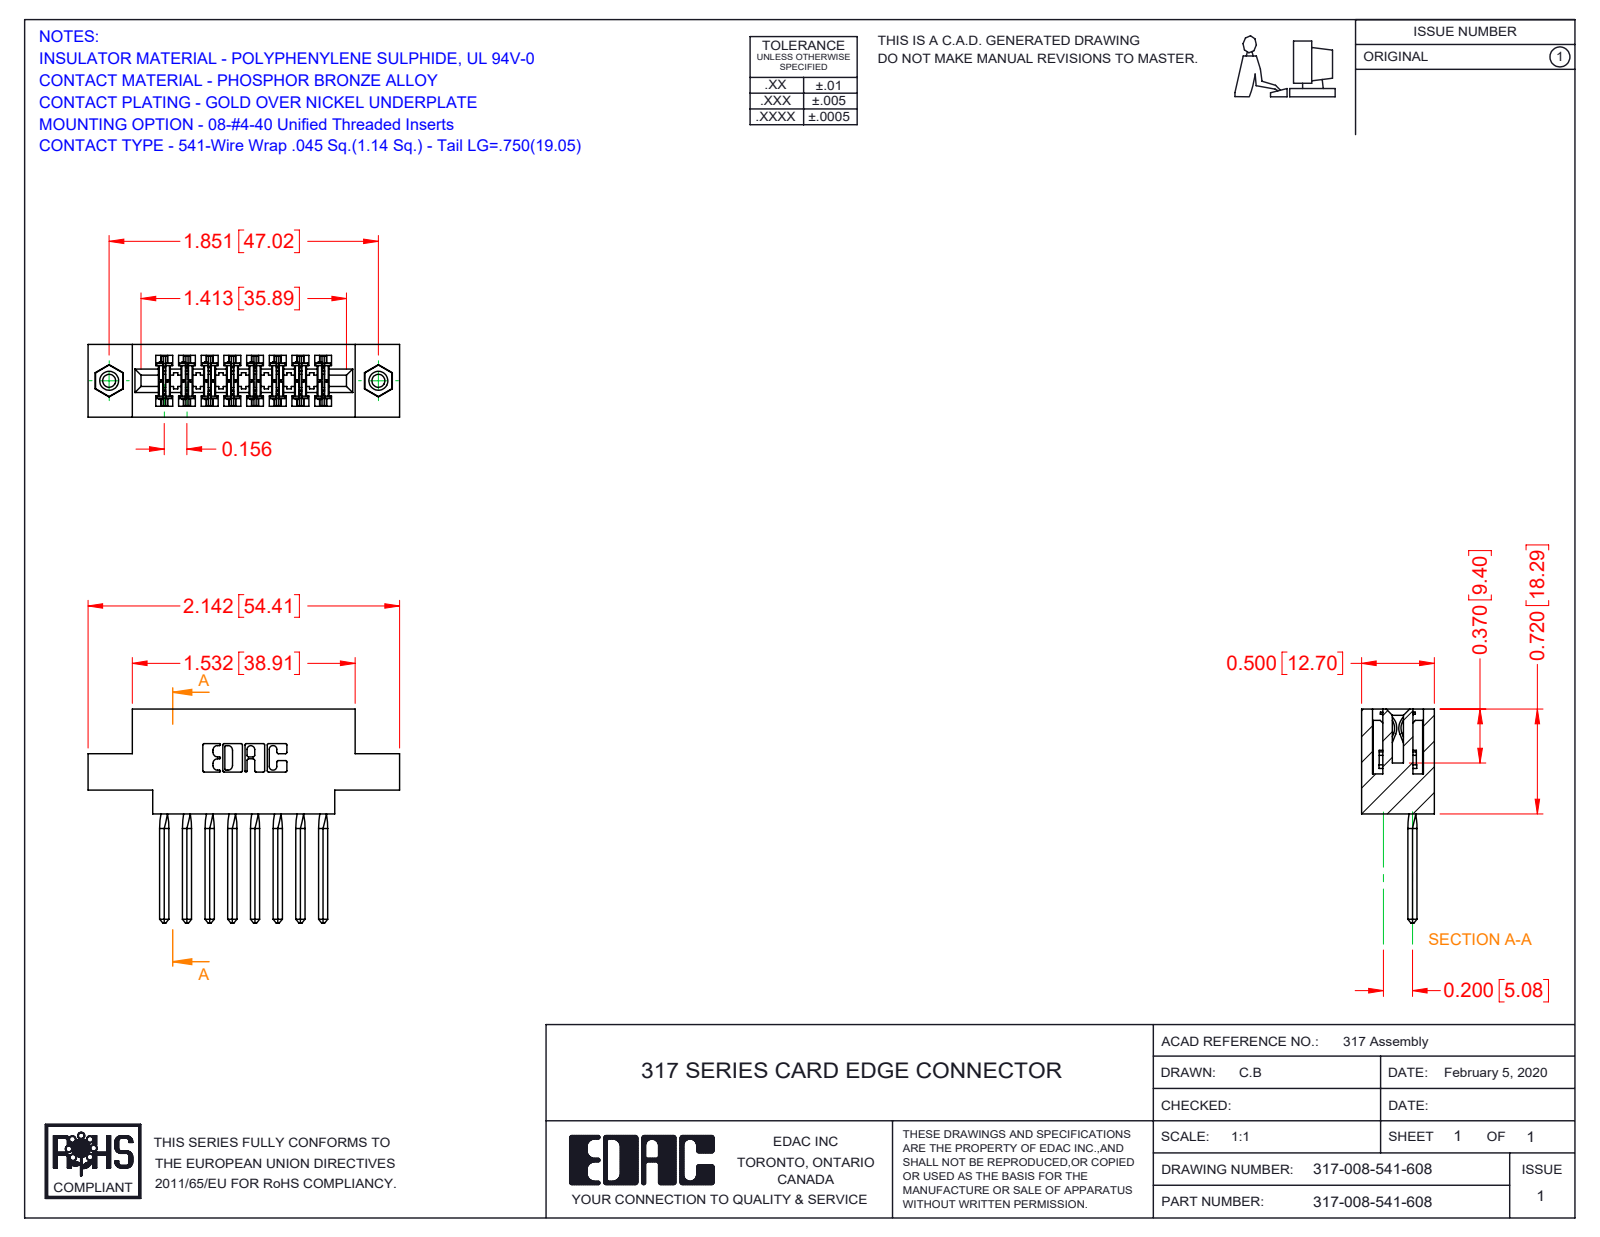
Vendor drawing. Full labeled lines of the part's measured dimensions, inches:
Part name (STEP PRODUCT): 317 Part_.156 Dia - TI; 317-008-541-608; 345-250-001_345-250-003-102; 317-290-002_541
STEP written by: SolidWorks 2016 (CONFIG_CONTROL_DESIGN)
Units: inches
Bodies: 11 solids, 1378 faces (1082 planar, 248 cylindrical, 48 other)
Overall size (bounding box): 2.142 × 1.47 × 0.5
Volume: 0.474 in³ · Surface area: 15.3 in²
Round holes (diameter × count): ⌀0.089 ×2, ⌀0.125 ×2, ⌀0.156 ×2
Round bosses / shafts (diameter × count): ⌀0.155 ×2
Partial cylindrical surfaces — rounded edges, fillets, slot ends (radius × count): R0.01 ×22, R0.015 ×16, R0.007 ×6, R0.031 ×6, R0.026 ×3, R0.095 ×2, R0.1 ×2, R0.11 ×2
Main face-to-face distances: 0.5, 0.075, 0.425, 0.11, 0.065, 0.22, 0.156, 0.331, 0.136, 0.116
Hole centre spacings: 1.851
